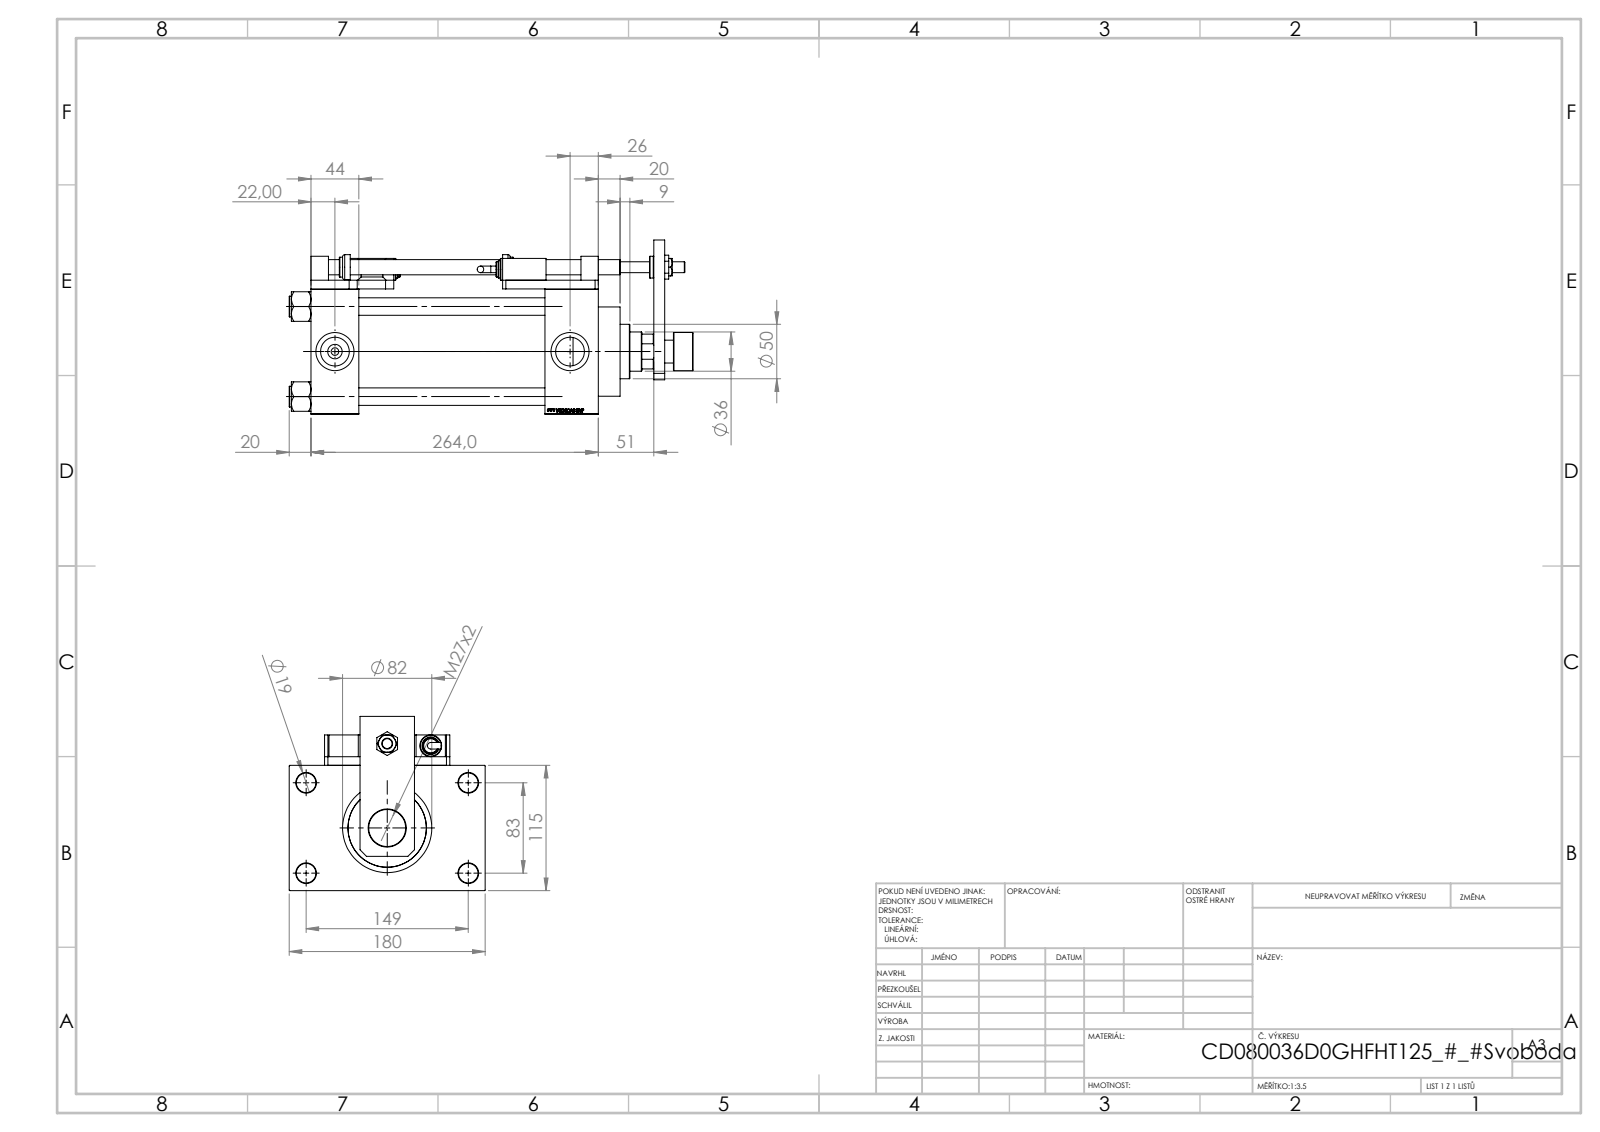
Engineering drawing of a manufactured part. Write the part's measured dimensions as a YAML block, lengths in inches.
part_name: "V215CD_SWITCH_Q_NUT; V215CD_SWITCH_Q_PODLOZKA_FRONT; V215CD_SWITCH_Q_TYC; V215CD_NUT_M5_D (+7 more)"
step_written_by: "SolidWorks 2019 (CONFIG_CONTROL_DESIGN)"
units: inches
bodies: {solids: 25, faces: 1393, planar: 670, cylindrical: 160, other: 563}
overall_size: [14.606, 7.087, 6.299]
volume: 157.9
surface_area: 752.9
round_holes:
  - {diameter: 0.335, count: 4}
  - {diameter: 0.531, count: 4}
  - {diameter: 0.63, count: 4}
  - {diameter: 0.709, count: 4}
  - {diameter: 0.276, count: 2}
  - {diameter: 1.041, count: 2}
  - {diameter: 1.378, count: 2}
  - {diameter: 0.394, count: 1}
  - {diameter: 0.551, count: 1}
  - {diameter: 1.004, count: 1}
  - {diameter: 1.063, count: 1}
  - {diameter: 1.417, count: 1}
round_bosses_or_shafts:
  - {diameter: 0.748, count: 4}
  - {diameter: 0.787, count: 3}
  - {diameter: 0.63, count: 2}
  - {diameter: 0.551, count: 2}
  - {diameter: 0.236, count: 2}
  - {diameter: 3.386, count: 1}
  - {diameter: 3.228, count: 1}
  - {diameter: 1.969, count: 1}
partial_cylinders:
  - {radius: 0.295, count: 4}
face_to_face_distances: [4.528, 0.315, 1.929, 8.661, 1.732, 10.394, 8.465, 6.732, 4.843, 1.28]
hole_center_spacings: [1.305, 2.302, 3.256, 3.357, 3.513, 4.561, 5.607, 1.26]
